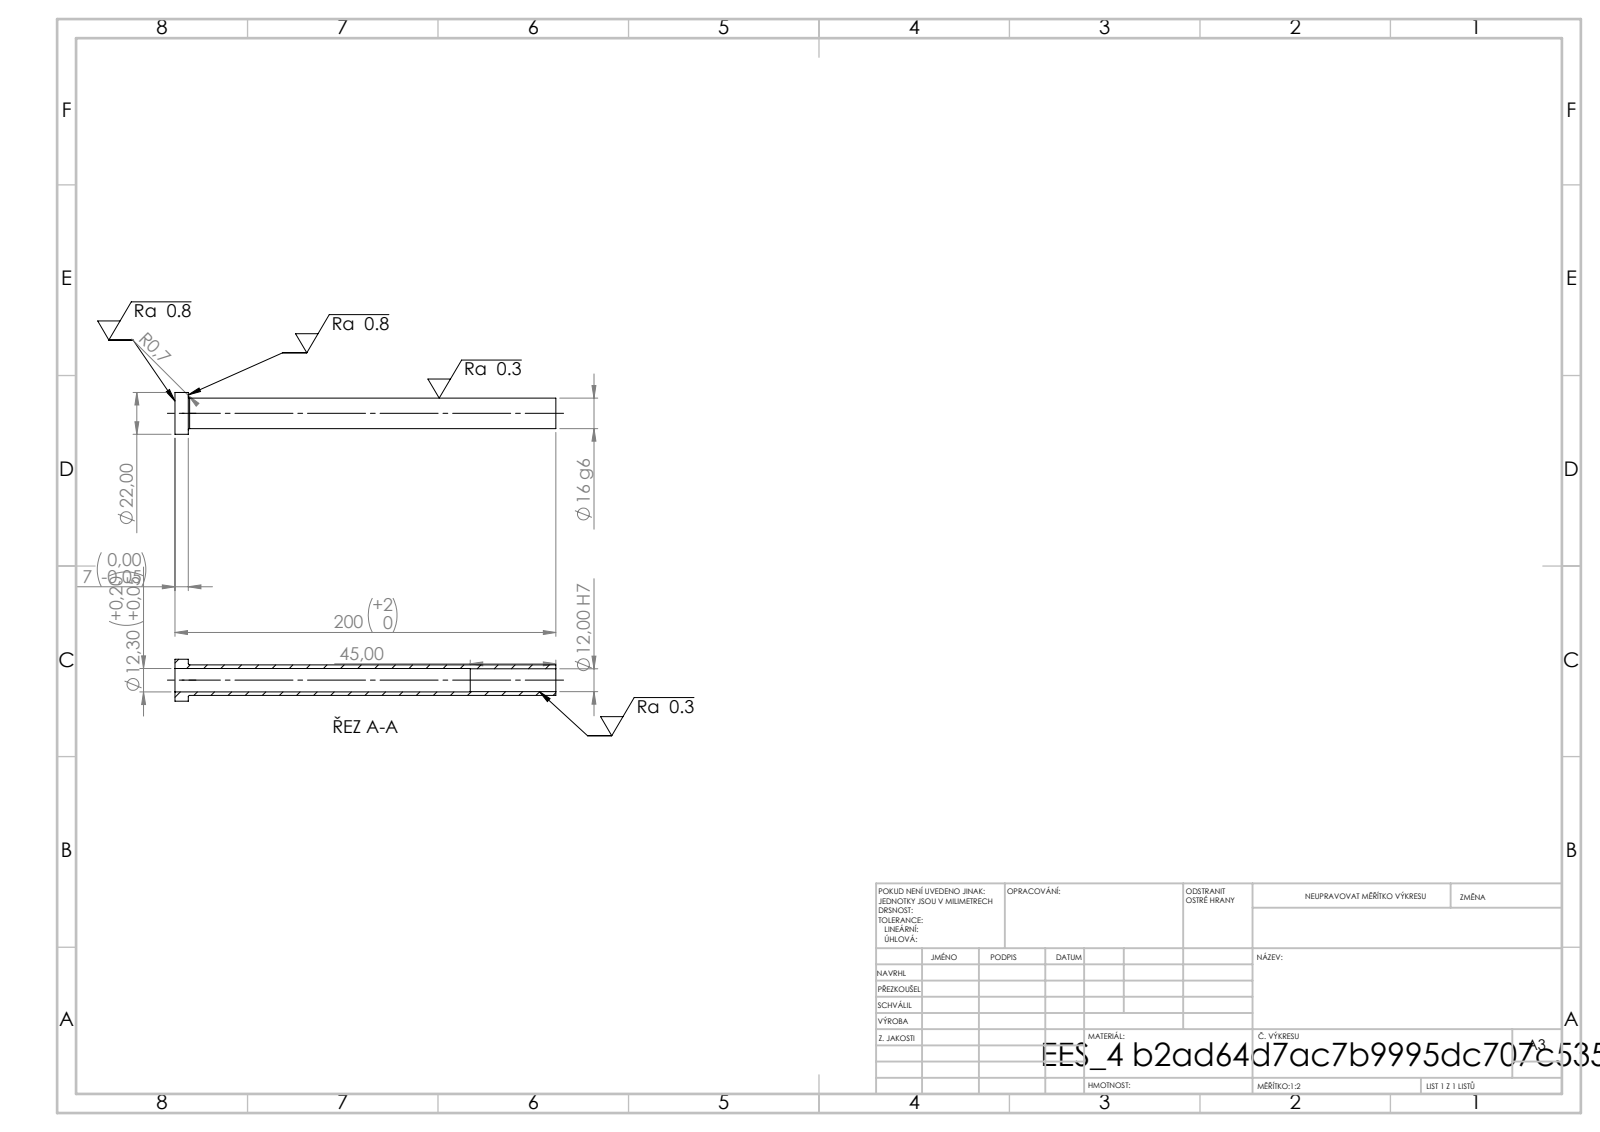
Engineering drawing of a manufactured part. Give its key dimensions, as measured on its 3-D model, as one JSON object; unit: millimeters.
{"step_written_by": "SolidWorks 2019 (CONFIG_CONTROL_DESIGN)", "units": "millimeters", "bodies": {"solids": 1, "faces": 14, "planar": 4, "cylindrical": 8, "other": 2}, "overall_size": [200, 22, 22], "volume_mm3": 17964, "surface_area_mm2": 18390, "round_holes": [[12, 1], [12.3, 1]], "round_bosses_or_shafts": [[22, 1], [16, 1]], "face_to_face_distances": [7, 200, 193, 155, 148, 45]}
